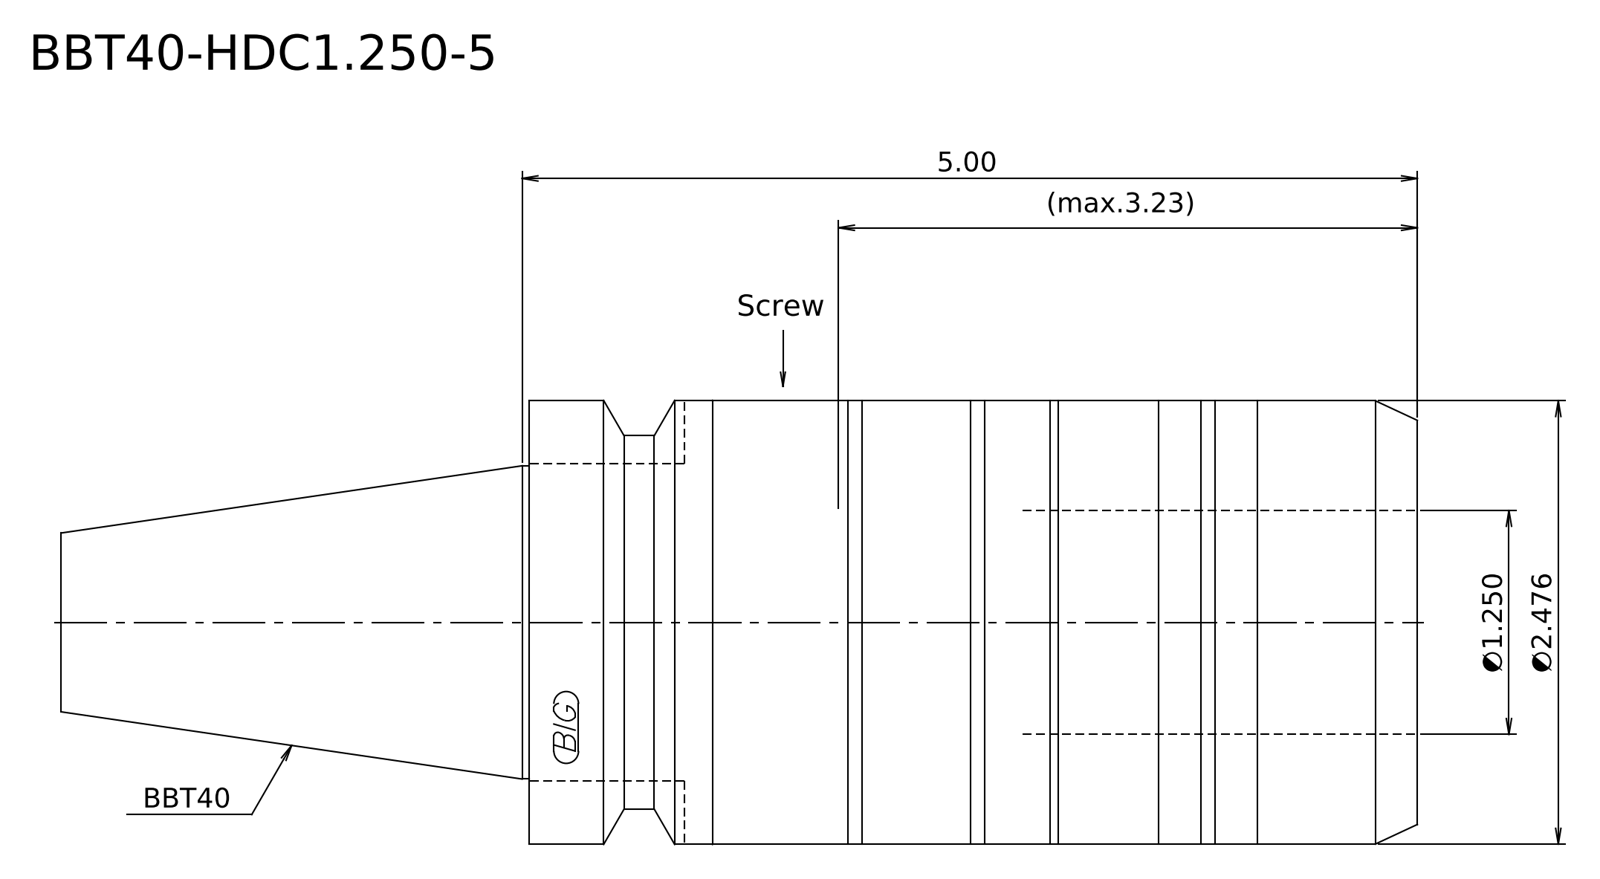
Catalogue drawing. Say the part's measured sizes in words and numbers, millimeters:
Its 3-D file was written by "Kubotek KeyCreator 2011 V10.0.2 (22737) (automotive_design)". It is 1 solid with 13 faces: 3 planar, 5 cylindrical and 5 other. Overall it measures 192.4 by 63 by 63 millimeters. Its volume is 449 297 cubic millimeters and its surface area 37 844 square millimeters. Round bosses or shafts: 1 of diameter 63, 1 of diameter 62.9, 1 of diameter 53, 1 of diameter 44.45. The main face-to-face distances are 126, 192.4, 66.4.
